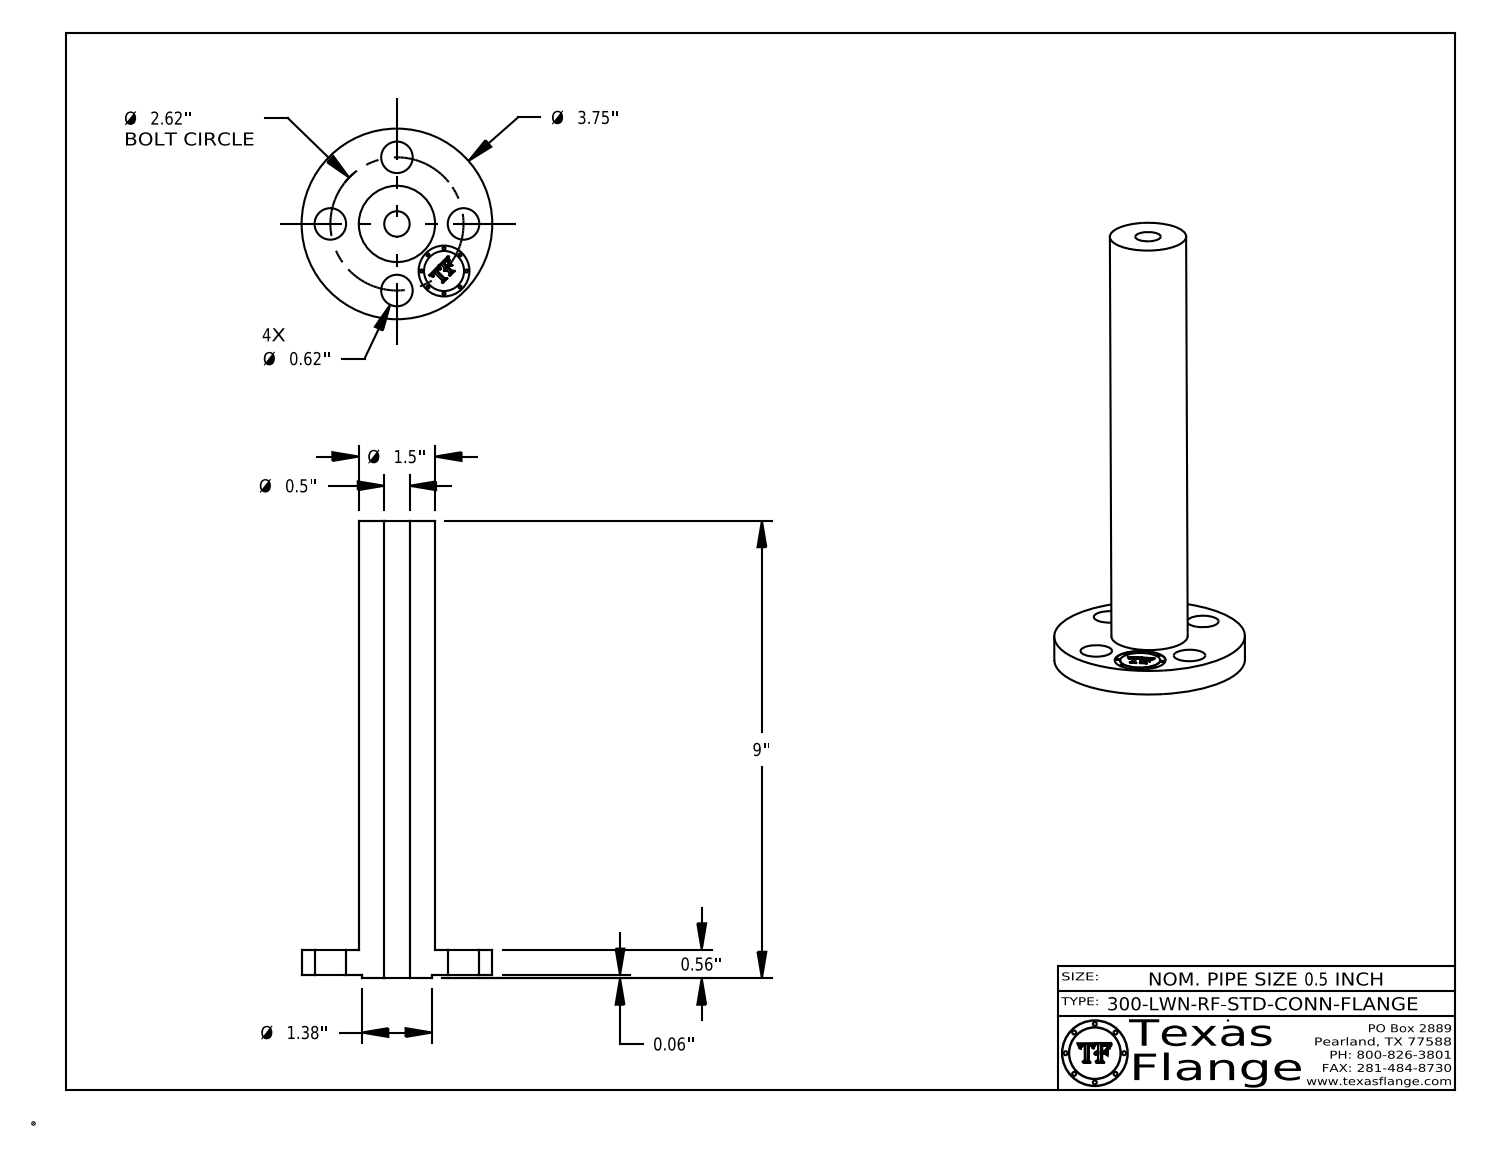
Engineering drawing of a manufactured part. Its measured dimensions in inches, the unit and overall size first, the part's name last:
Units: inches
Overall size (bounding box): 9 × 3.75 × 3.75
Round holes (diameter × count): ⌀0.62 ×4, ⌀0.5 ×1, ⌀1 ×1
Round bosses / shafts (diameter × count): ⌀0.061 ×8, ⌀3.75 ×1, ⌀1.5 ×1, ⌀1.38 ×1, ⌀0.788 ×1
Main face-to-face distances: 0.498, 8.937, 8.44, 0.063, 0.56, 9, 0.555, 0.493, 8.445, 0.298
Hole centre spacings: 1.31, 1.852, 1.003, 2.42, 2.62, 1.31
Volume: 18.13 in³ · Surface area: 83.26 in²
Bodies: 1 solid, 405 faces (369 planar, 36 cylindrical, 0 other)
Part name (STEP PRODUCT): 0.5-300-LWN-RF-STD-CONN-FLANGE
STEP written by: CATIA V5 STEP AP214 (AUTOMOTIVE_DESIGN)
